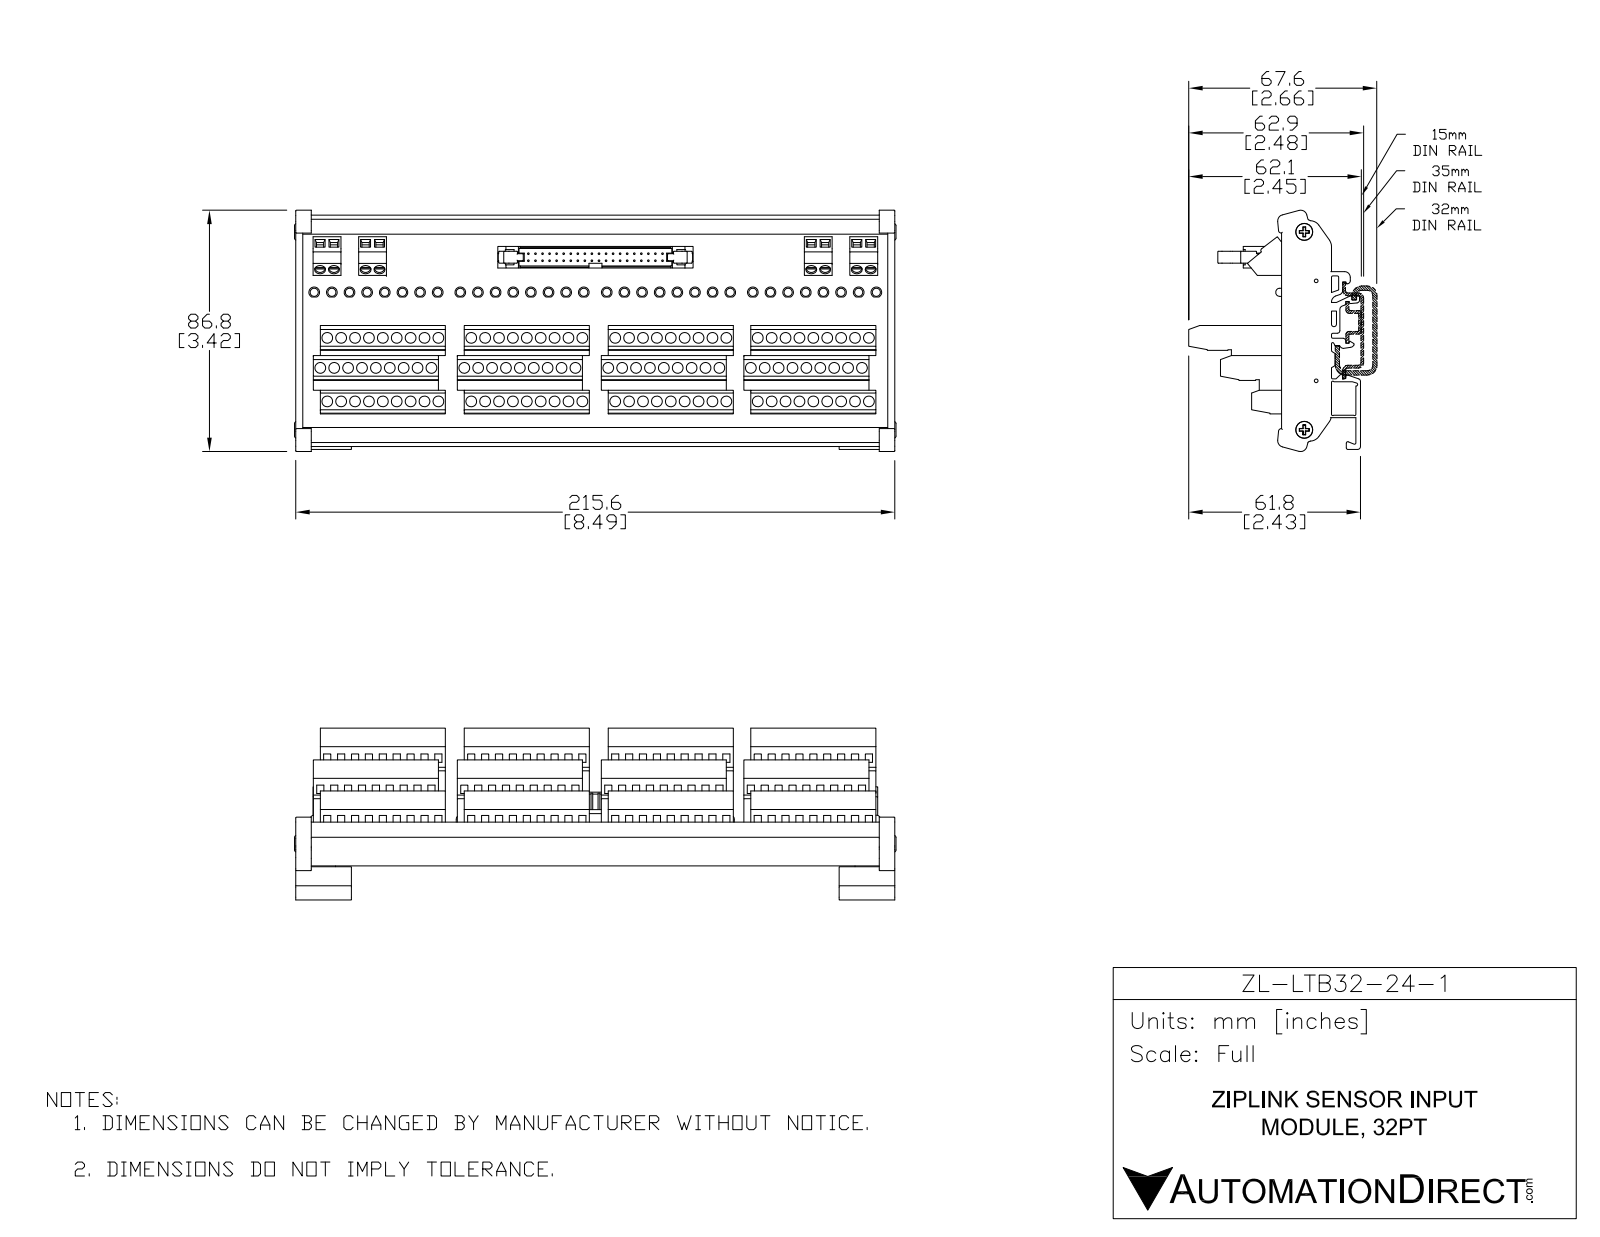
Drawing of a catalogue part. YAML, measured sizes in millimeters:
part_name: "ZL-LTB32-24-1"
step_written_by: "SolidWorks 2016 (AUTOMOTIVE_DESIGN)"
units: millimeters
bodies: {solids: 115, faces: 4770, planar: 2908, cylindrical: 1705, other: 157}
overall_size: [216.5, 86.83, 61.78]
volume: 241052
surface_area: 193511
round_holes:
  - {diameter: 1.4, count: 116}
  - {diameter: 3.87, count: 108}
  - {diameter: 0.25, count: 64}
  - {diameter: 0.83, count: 40}
  - {diameter: 0.3, count: 8}
  - {diameter: 3.91, count: 8}
  - {diameter: 1.33, count: 2}
  - {diameter: 1.5, count: 2}
  - {diameter: 1.65, count: 2}
  - {diameter: 2.5, count: 2}
  - {diameter: 3.5, count: 2}
  - {diameter: 6.1, count: 2}
round_bosses_or_shafts:
  - {diameter: 1.6, count: 108}
  - {diameter: 0.85, count: 40}
  - {diameter: 0.62, count: 40}
  - {diameter: 3.85, count: 32}
  - {diameter: 2.94, count: 32}
  - {diameter: 3.81, count: 8}
  - {diameter: 5.5, count: 2}
  - {diameter: 4, count: 2}
partial_cylinders:
  - {radius: 0.5, count: 62}
  - {radius: 0.51, count: 50}
  - {radius: 0.2, count: 47}
  - {radius: 0.25, count: 24}
  - {radius: 0.3, count: 10}
  - {radius: 0.9, count: 5}
  - {radius: 0.98, count: 5}
  - {radius: 1.26, count: 5}
face_to_face_distances: [1.5, 5.41, 1.52, 6.04, 4.52, 6.91, 11.43, 12.95, 6.02, 7.54]
hole_center_spacings: [5, 15.44, 10.46, 51.82, 16.38, 176.78, 25.4, 25.89]
